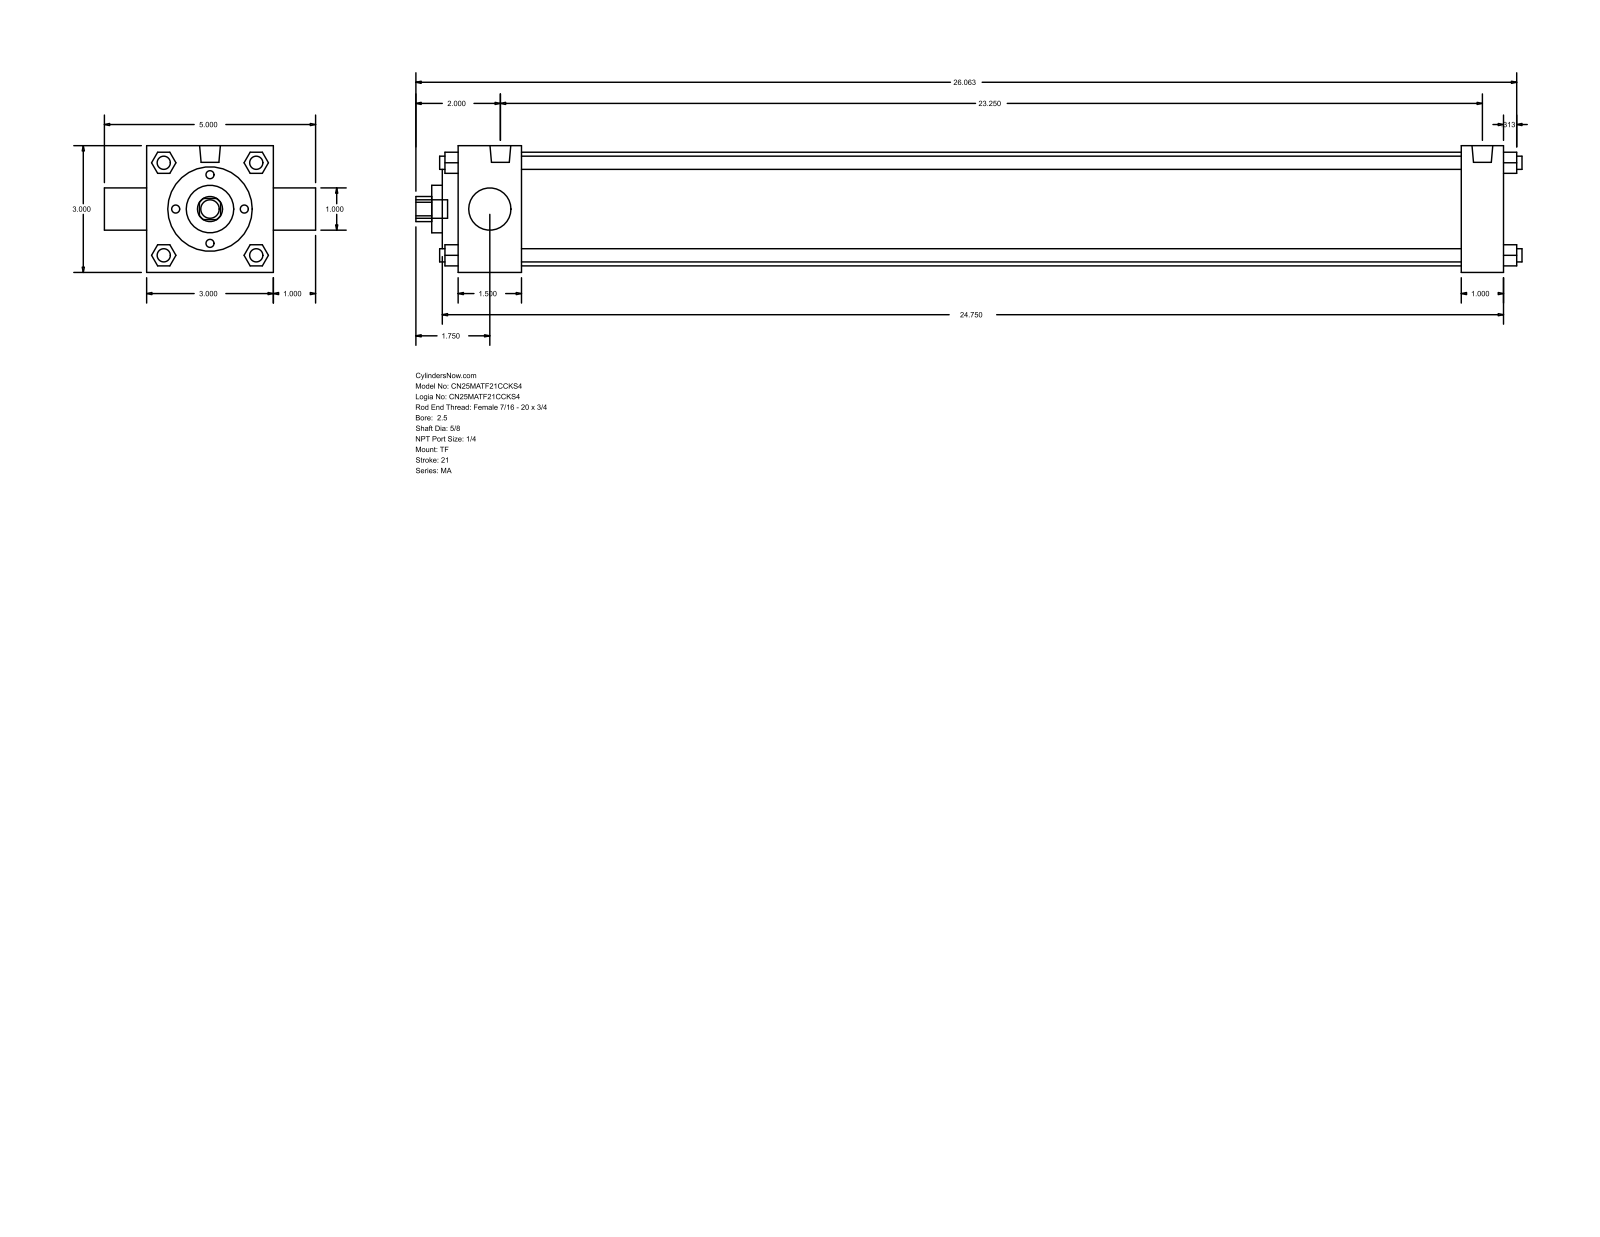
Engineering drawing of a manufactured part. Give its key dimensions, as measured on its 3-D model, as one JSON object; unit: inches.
{"part_name": "MA_TF__0250_0.625", "step_written_by": "GSSL Pune (CONFIG_CONTROL_DESIGN)", "units": "inches", "bodies": {"solids": 0, "faces": 122, "planar": 93, "cylindrical": 29, "other": 0}, "overall_size": [26.187, 5, 3], "round_holes": [[0.625, 1], [1, 1], [1.125, 1], [2, 1], [2.69, 1]], "round_bosses_or_shafts": [[0.313, 7], [0.492, 2], [0.437, 1]], "partial_cylinders_radius": [[0.297, 1]], "face_to_face_distances": [3, 24.75, 1, 1.5, 23.75, 22.25, 23.25, 0.5, 0.375, 1.875]}
